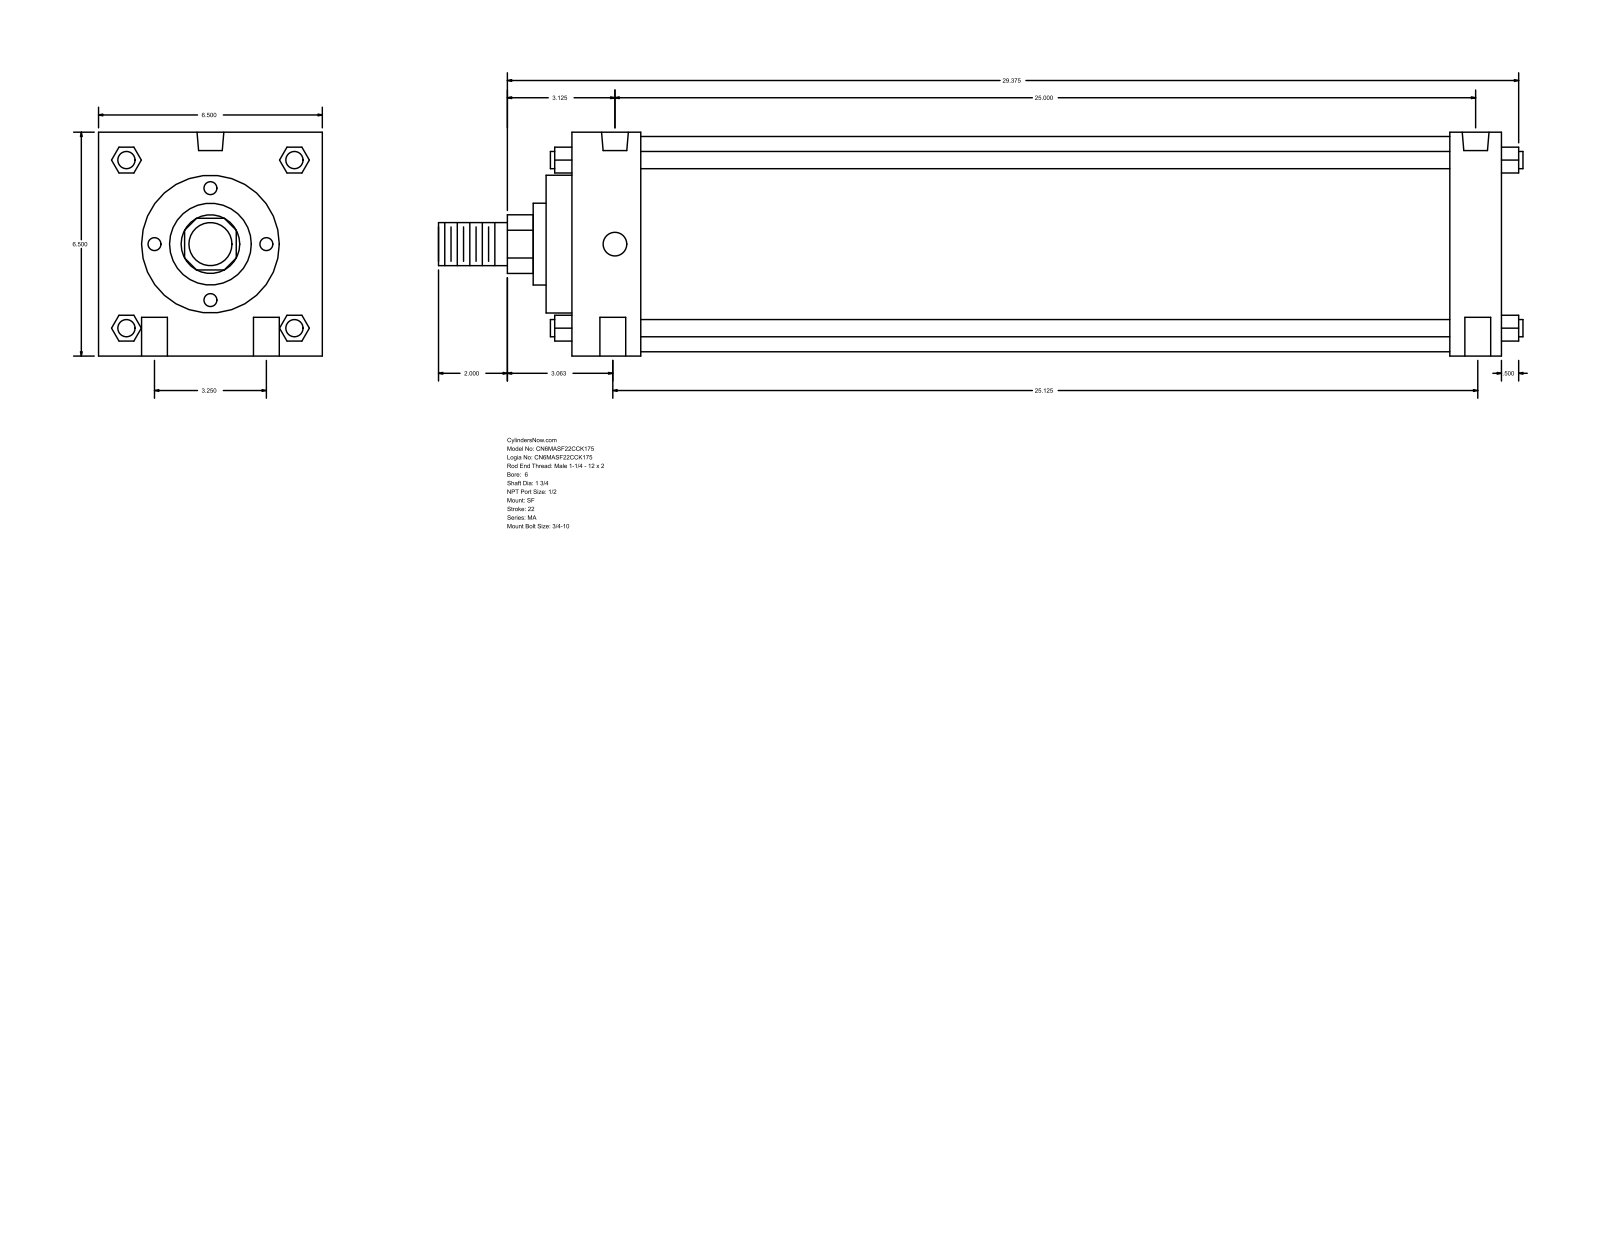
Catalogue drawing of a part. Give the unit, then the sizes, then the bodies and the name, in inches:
Units: inches
Overall size (bounding box): 31.5 × 6.5 × 6.5
Round holes (diameter × count): ⌀0.75 ×4, ⌀0.687 ×2, ⌀0.778 ×2
Round bosses / shafts (diameter × count): ⌀0.5 ×4, ⌀6.25 ×1, ⌀4 ×1, ⌀2.375 ×1, ⌀1.75 ×1, ⌀1.25 ×1
Partial cylindrical surfaces — rounded edges, fillets, slot ends (radius × count): R0.852 ×1
Main face-to-face distances: 6.5, 27, 0.75, 2, 25.5, 1.5, 23.5, 25, 2.75, 26.25
Hole centre spacings: 1.626, 3.25, 25, 25.115, 25.115, 25.125, 25.334
Bodies: 0 solids, 126 faces (95 planar, 31 cylindrical, 0 other)
Part name (STEP PRODUCT): MA_SF__0600_1.75
STEP written by: GSSL Pune (CONFIG_CONTROL_DESIGN)
